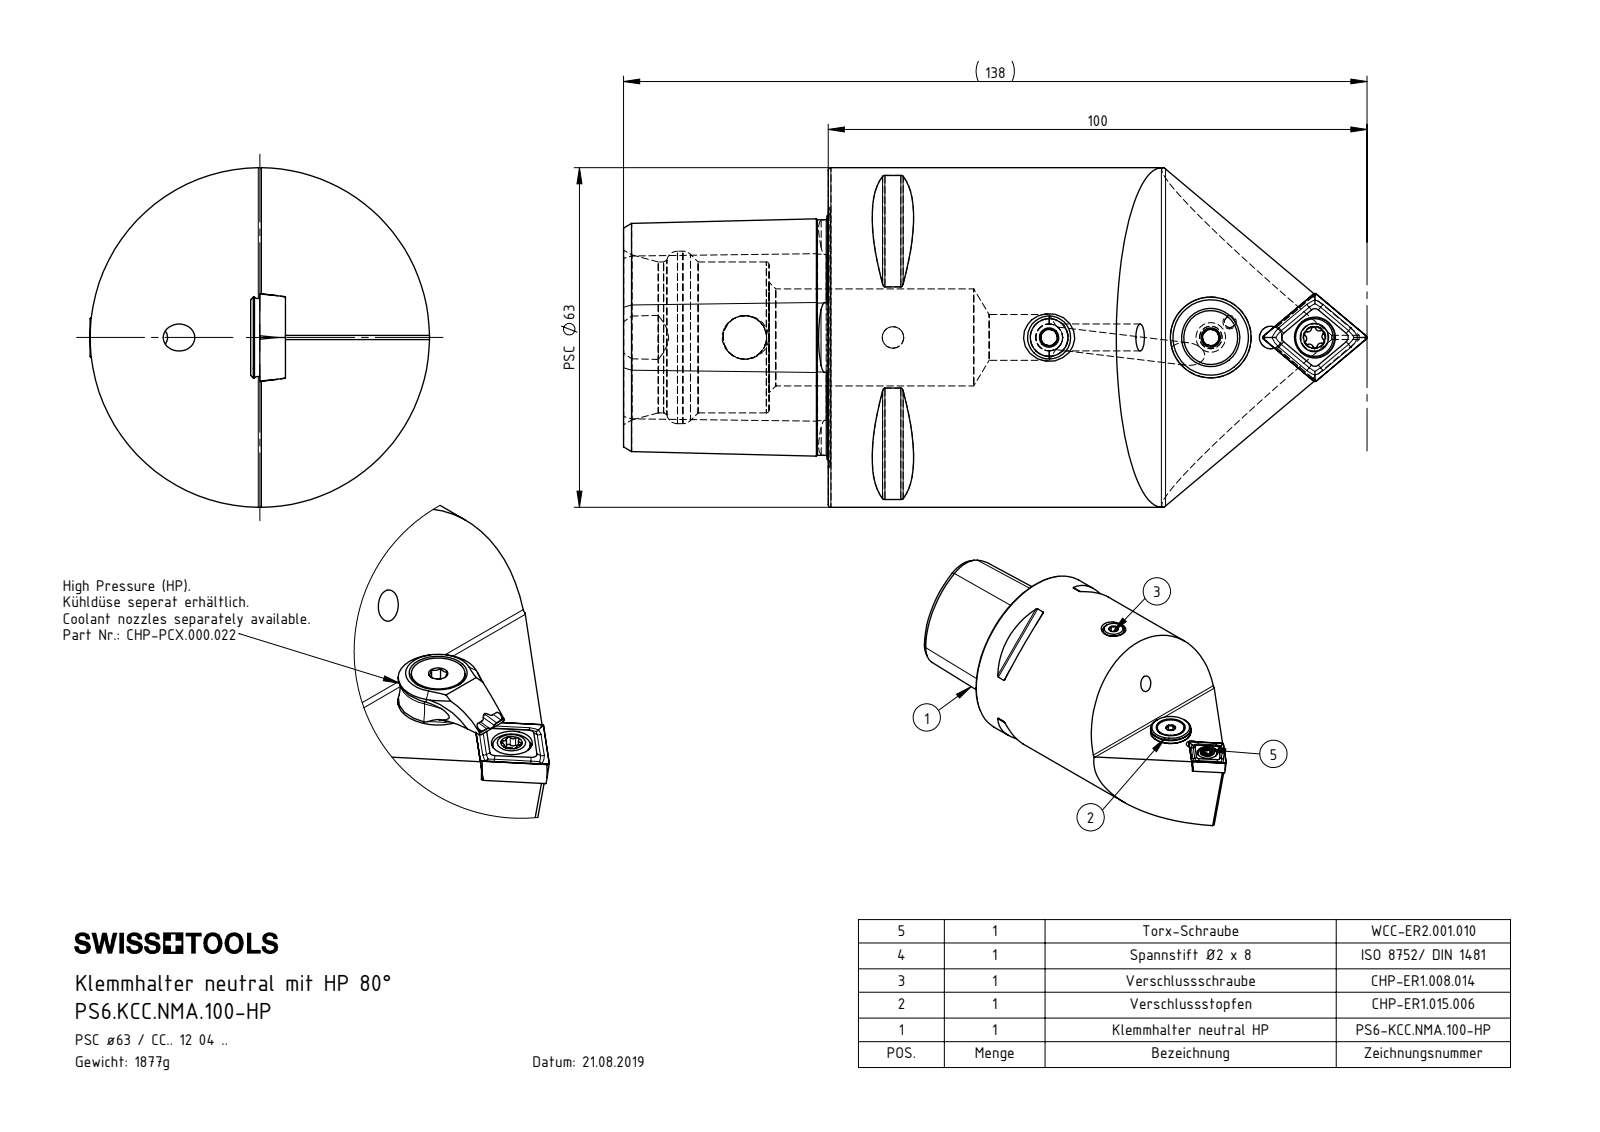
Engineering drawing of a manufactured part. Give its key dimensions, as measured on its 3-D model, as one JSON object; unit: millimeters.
{"part_name": "DIN 3771 - 13x1; CHP-ER1.015.006_A; PS6-KCC.NMA.100-HP_A; WCC-ER2.001.010_A (+6 more)", "step_written_by": "SolidWorks 2017 (AUTOMOTIVE_DESIGN)", "units": "millimeters", "bodies": {"solids": 8, "faces": 260, "planar": 86, "cylindrical": 59, "other": 115}, "overall_size": [137.78, 63.13, 63], "volume_mm3": 237307, "surface_area_mm2": 36255, "round_holes": [[4.2, 4], [5, 2], [1.2, 1], [2, 1], [2.5, 1], [3, 1], [4, 1], [5.2, 1], [5.5, 1], [7, 1], [7.6, 1], [8.1, 1]], "round_bosses_or_shafts": [[5, 2], [63, 1], [15, 1], [13.4, 1], [10, 1], [8, 1], [7, 1], [5.5, 1]], "partial_cylinders_radius": [[0.5, 10], [0.39, 6], [0.69, 3], [0.69, 3], [6, 1], [7, 1]], "face_to_face_distances": [55, 38, 93, 24.88, 4.5, 27, 11, 66, 4.46, 55.8], "hole_center_spacings": [4.5, 8.1, 8.2, 8.83, 12.25, 16.91, 17.01, 20.28]}
